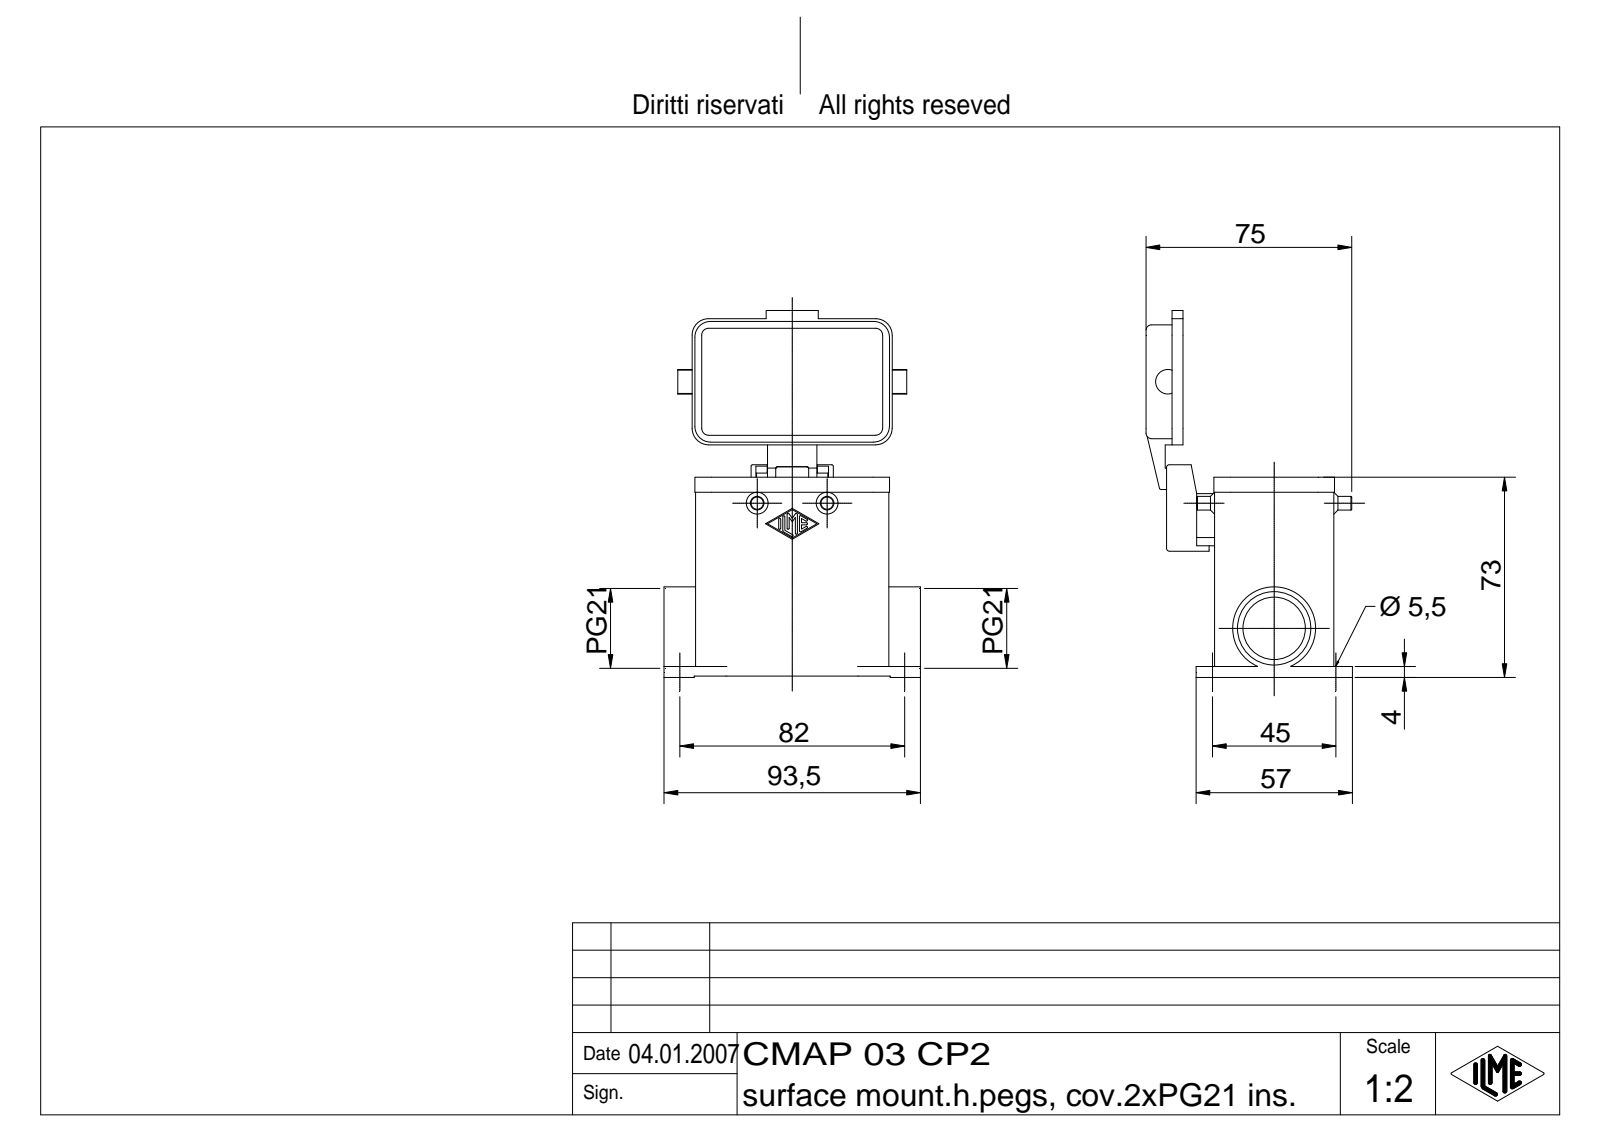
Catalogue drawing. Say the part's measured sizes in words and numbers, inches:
The part is named "CMAP 03 CP2". Its 3-D file was written by "Autodesk Inventor 7 (AUTOMOTIVE_DESIGN)". It is 1 solid with 469 faces: 193 planar, 166 cylindrical and 110 other. Overall it measures 5.266 by 3.681 by 2.963 inches. Its volume is 6.333 cubic inches and its surface area 94.11 square inches. Round holes: 4 of diameter 0.217, 1 of diameter 0.157, 1 of diameter 0.197, 1 of diameter 0.897, 1 of diameter 1.054. Round bosses or shafts: 2 of diameter 0.197, 2 of diameter 0.118, 1 of diameter 1.192, 1 of diameter 0.276, 1 of diameter 0.157. Partial cylindrical surfaces (rounded edges, fillets, slot ends): 14 of radius 0.015, 14 of radius 0.039, 12 of radius 0.236, 10 of radius 0.02, 8 of radius 0.028, 8 of radius 0.079, 4 of radius 0.098, 4 of radius 0.118. The main face-to-face distances are 0.118, 1.594, 1.713, 0.098, 2.697, 1.476, 0.886, 2.598, 0.138, 2.48. The hole center spacings are 1.772, 3.228, 3.683.
